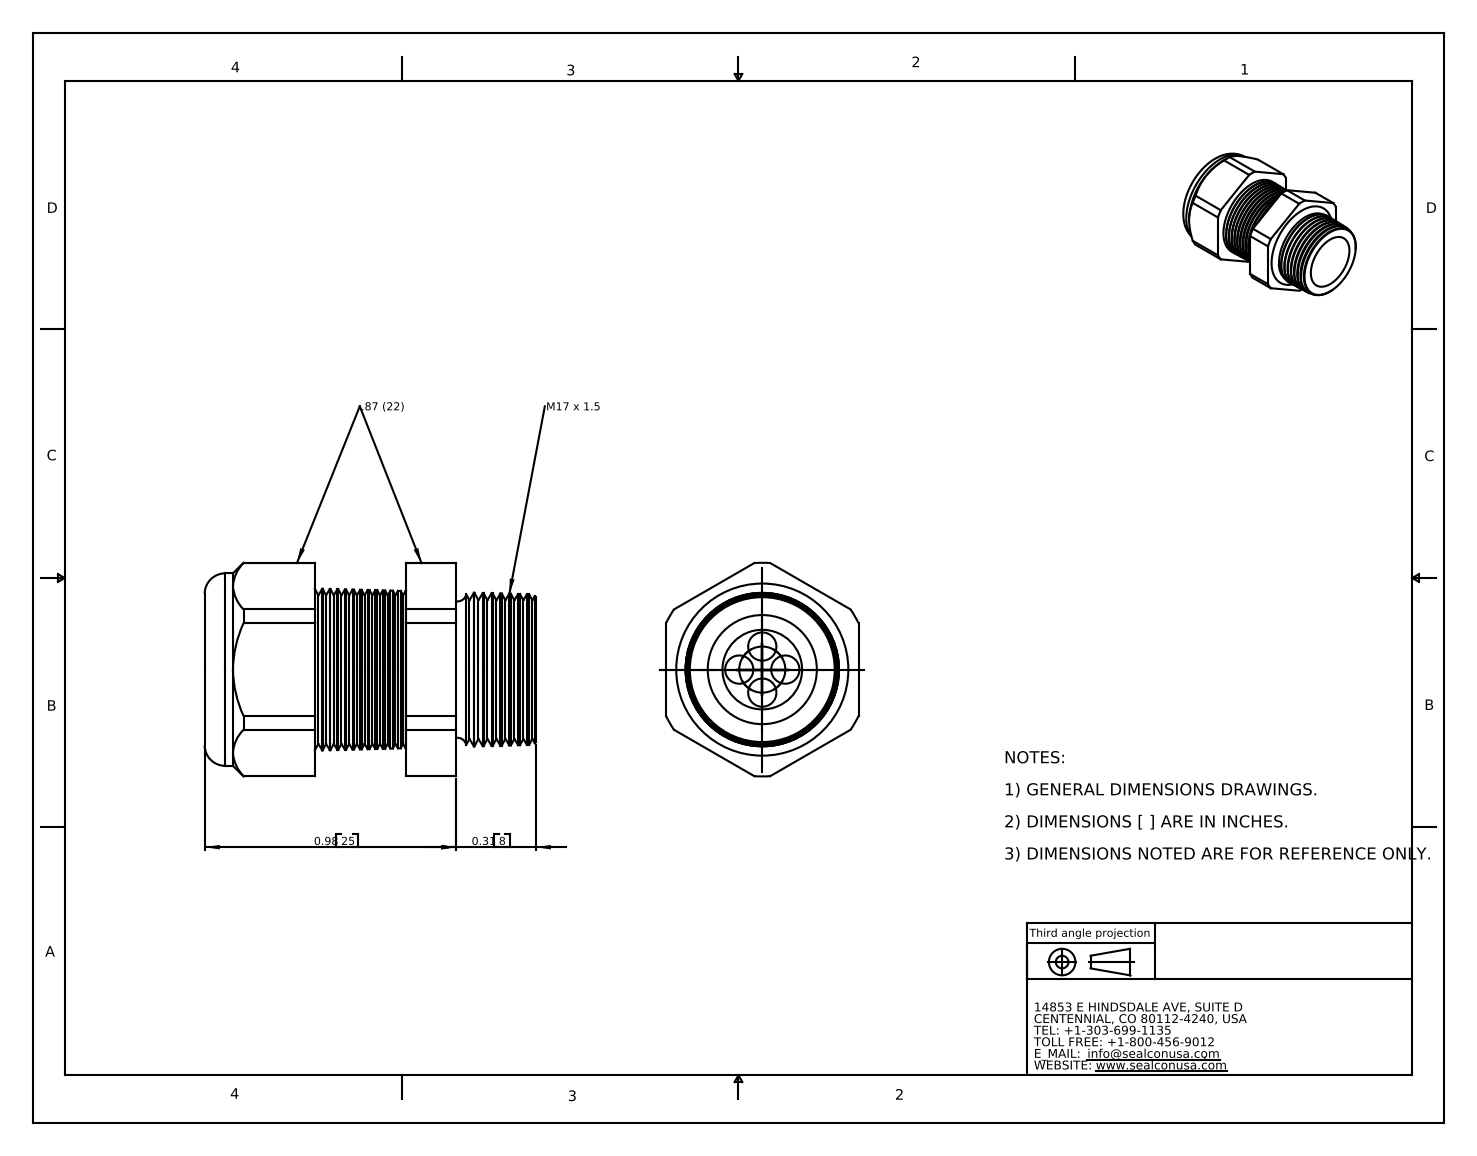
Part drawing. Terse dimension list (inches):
name: CD17M5-GY
written by: SolidWorks 2007 (CONFIG_CONTROL_DESIGN)
unit: in
bodies: 2 solids, 187 faces (21 planar, 28 cylindrical, 138 other)
size: 1.29 × 0.833 × 0.75
volume: 0.352 in³; area: 6.703 in²
holes: 4× ⌀0.11, 1× ⌀0.29, 1× ⌀0.31
bosses: 1× ⌀0.75
rounds: 1× R0.416
face distances: 0.75, 0.75, 0.783, 0.429, 0.354, 0.98, 0.551, 0.197, 1.29, 0.861
hole spacings: 0.09, 0.127, 0.18
